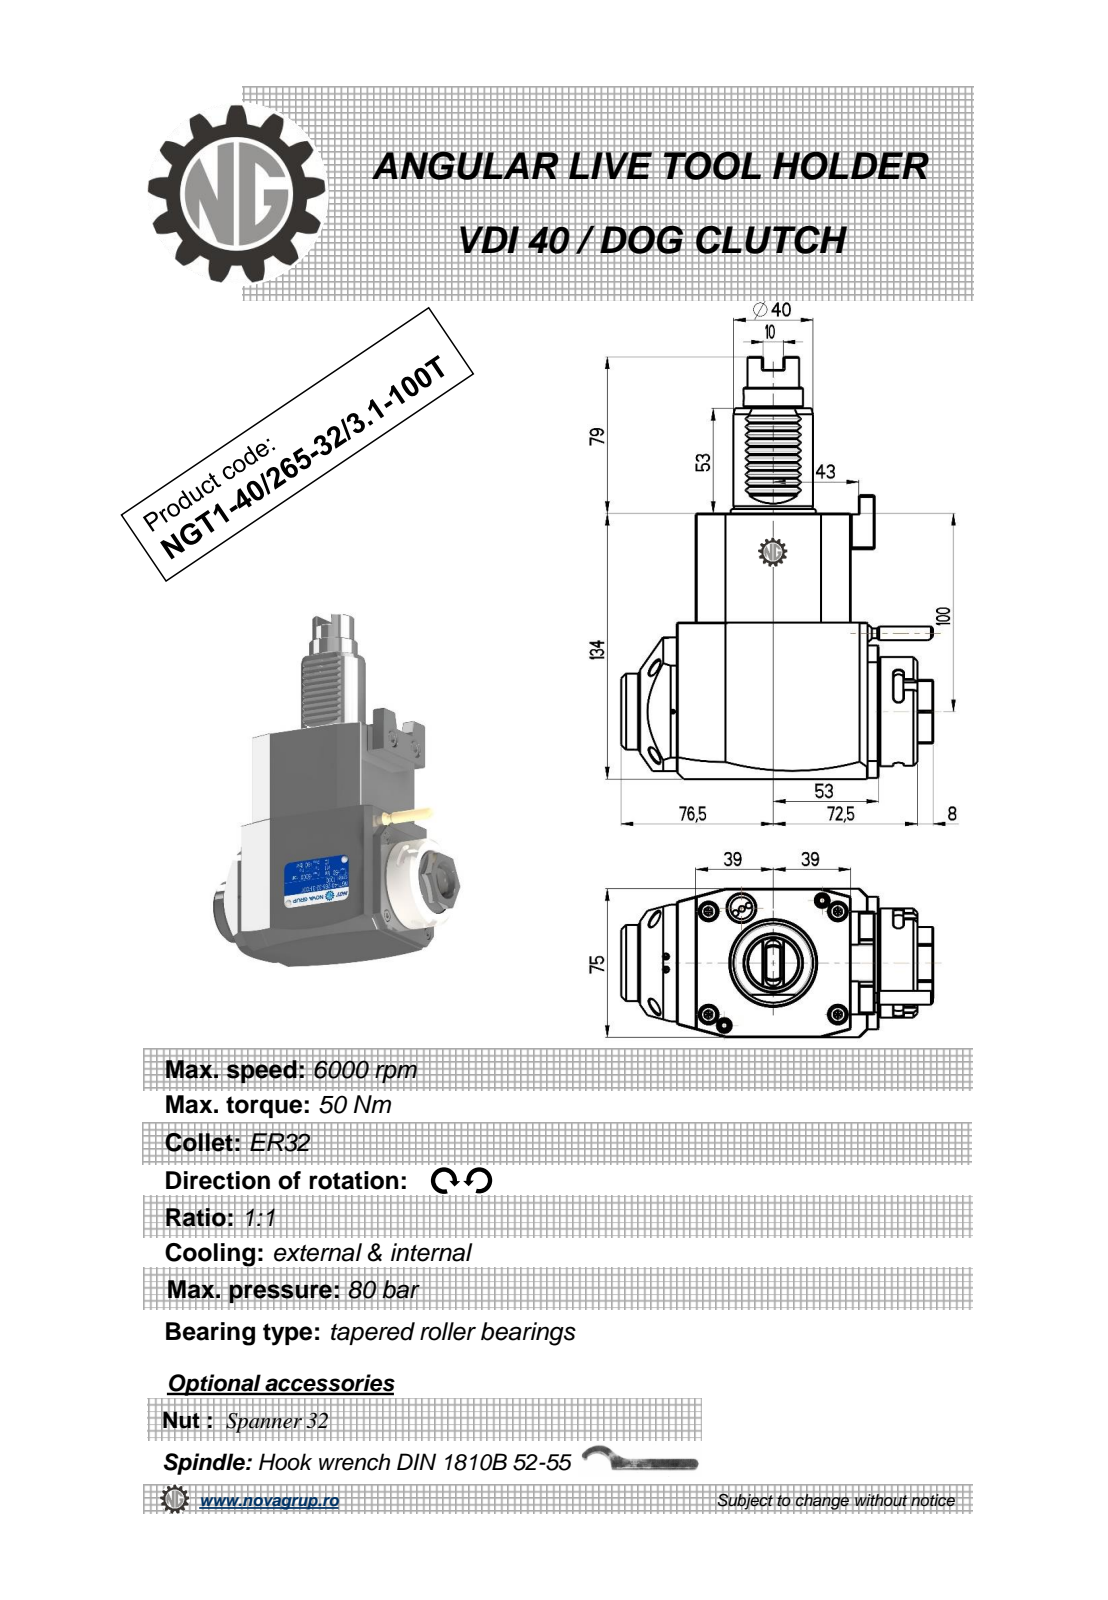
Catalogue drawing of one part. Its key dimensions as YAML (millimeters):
part_name: "NGT1_40_265_32_3_1_100T"
step_written_by: "PRO/ENGINEER BY PARAMETRIC TECHNOLOGY CORPORATION, 2010280 (CONFIG_CONTROL_DESIGN)"
units: millimeters
bodies: {solids: 1, faces: 339, planar: 210, cylindrical: 65, other: 64}
overall_size: [213, 157, 75]
volume: 1094000
surface_area: 78787
round_holes:
  - {diameter: 2.5, count: 1}
  - {diameter: 3, count: 1}
  - {diameter: 4.2, count: 1}
  - {diameter: 23, count: 1}
round_bosses_or_shafts:
  - {diameter: 55, count: 1}
  - {diameter: 48, count: 1}
  - {diameter: 40, count: 1}
  - {diameter: 38.5, count: 1}
  - {diameter: 30, count: 1}
  - {diameter: 26, count: 1}
  - {diameter: 8, count: 1}
  - {diameter: 7, count: 1}
partial_cylinders:
  - {radius: 0.3, count: 10}
  - {radius: 0.26, count: 6}
  - {radius: 2.5, count: 6}
  - {radius: 0.5, count: 3}
  - {radius: 1, count: 2}
  - {radius: 180, count: 2}
  - {radius: 12.5, count: 1}
  - {radius: 24.5, count: 1}
face_to_face_distances: [75, 134, 78, 14, 92, 19.5, 84.88, 111.5, 33.5, 4]
hole_center_spacings: [43.2, 120.28, 158.5]
